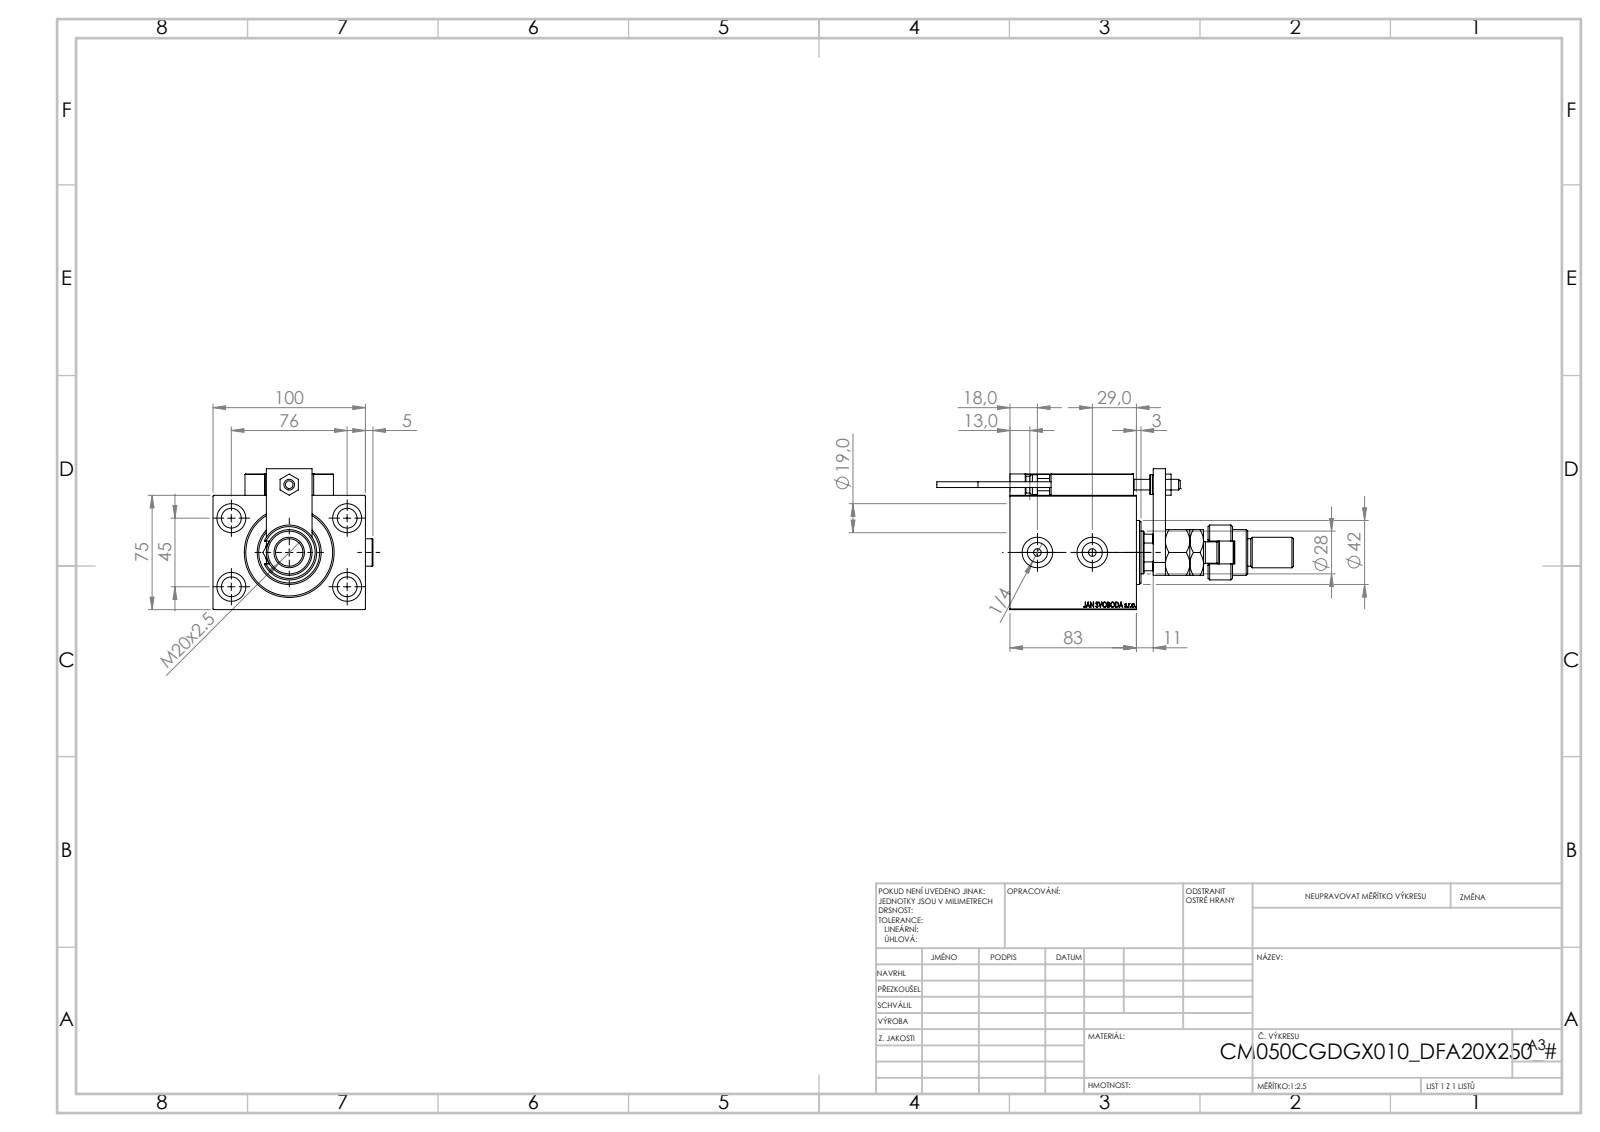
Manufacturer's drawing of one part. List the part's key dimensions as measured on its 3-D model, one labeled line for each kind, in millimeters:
Part name (STEP PRODUCT): MAGNET; KONCOVKA; ALLEN BOLT D5; MFA (+8 more)
STEP written by: SolidWorks 2019 (CONFIG_CONTROL_DESIGN)
Units: millimetres
Bodies: 27 solids, 1422 faces (623 planar, 217 cylindrical, 582 other)
Overall size (bounding box): 234 × 104.9 × 92.5
Volume: 646 942 mm³ · Surface area: 133 627 mm²
Round holes (diameter × count): ⌀8 ×5, ⌀3.2 ×4, ⌀4 ×4, ⌀5 ×4, ⌀13 ×4, ⌀19 ×4, ⌀20 ×3, ⌀13.16 ×2, ⌀7 ×1, ⌀18.5 ×1, ⌀28 ×1, ⌀31.5 ×1
Round bosses / shafts (diameter × count): ⌀18 ×3, ⌀5 ×2, ⌀3.8 ×2, ⌀42 ×1, ⌀36 ×1, ⌀30 ×1, ⌀22 ×1, ⌀14 ×1
Partial cylindrical surfaces — rounded edges, fillets, slot ends (radius × count): R0.3 ×30, R3 ×2, R7.5 ×1, R12 ×1, R13.5 ×1
Main face-to-face distances: 75, 100, 32, 83, 70, 51, 8, 19, 14, 10
Hole centre spacings: 44.16, 11.37, 20, 29.59, 29.69, 35.06, 36.06, 41.34
